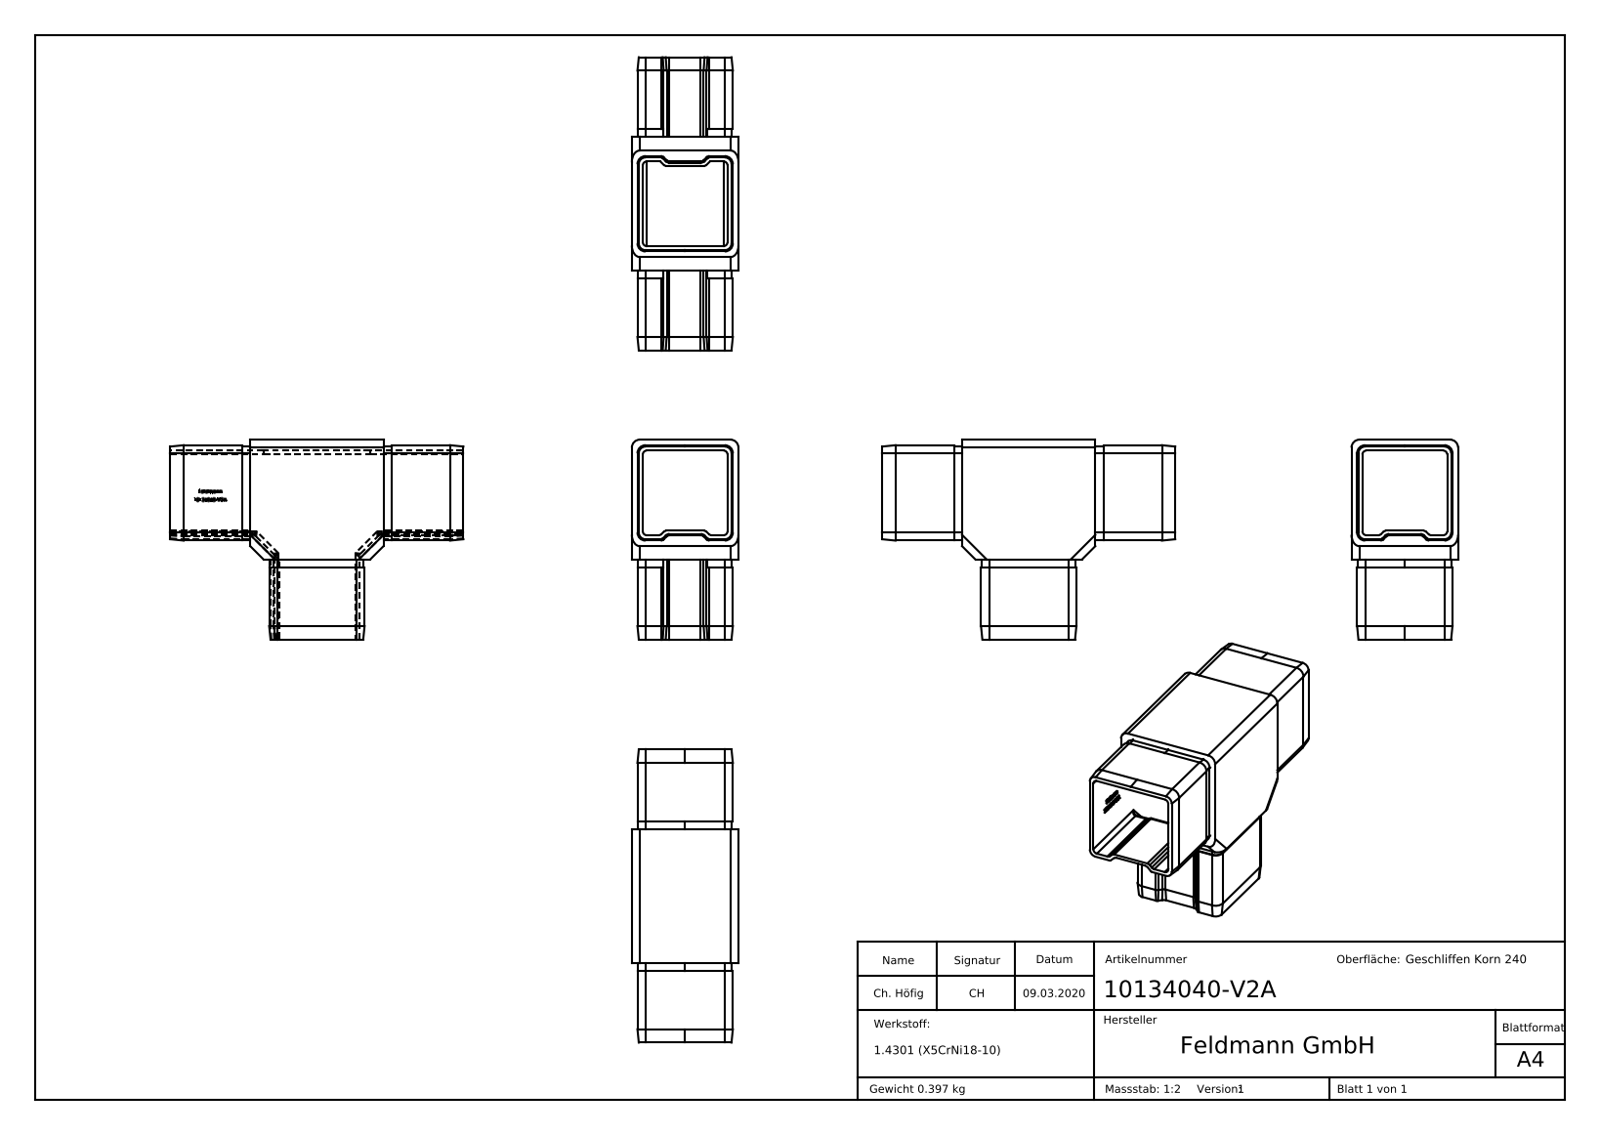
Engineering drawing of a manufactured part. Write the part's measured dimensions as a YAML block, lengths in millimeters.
part_name: "10134040-V2A"
step_written_by: "SolidWorks 2015 (CONFIG_CONTROL_DESIGN)"
units: millimeters
bodies: {solids: 1, faces: 506, planar: 283, cylindrical: 86, other: 137}
overall_size: [110, 75, 40]
volume: 50240
surface_area: 38818
partial_cylinders:
  - {radius: 1.5, count: 39}
  - {radius: 3, count: 14}
  - {radius: 2.7, count: 8}
face_to_face_distances: [2, 33.8, 31.8, 4.1, 2.1, 35.9, 37.9, 35.8, 1.7, 40]
